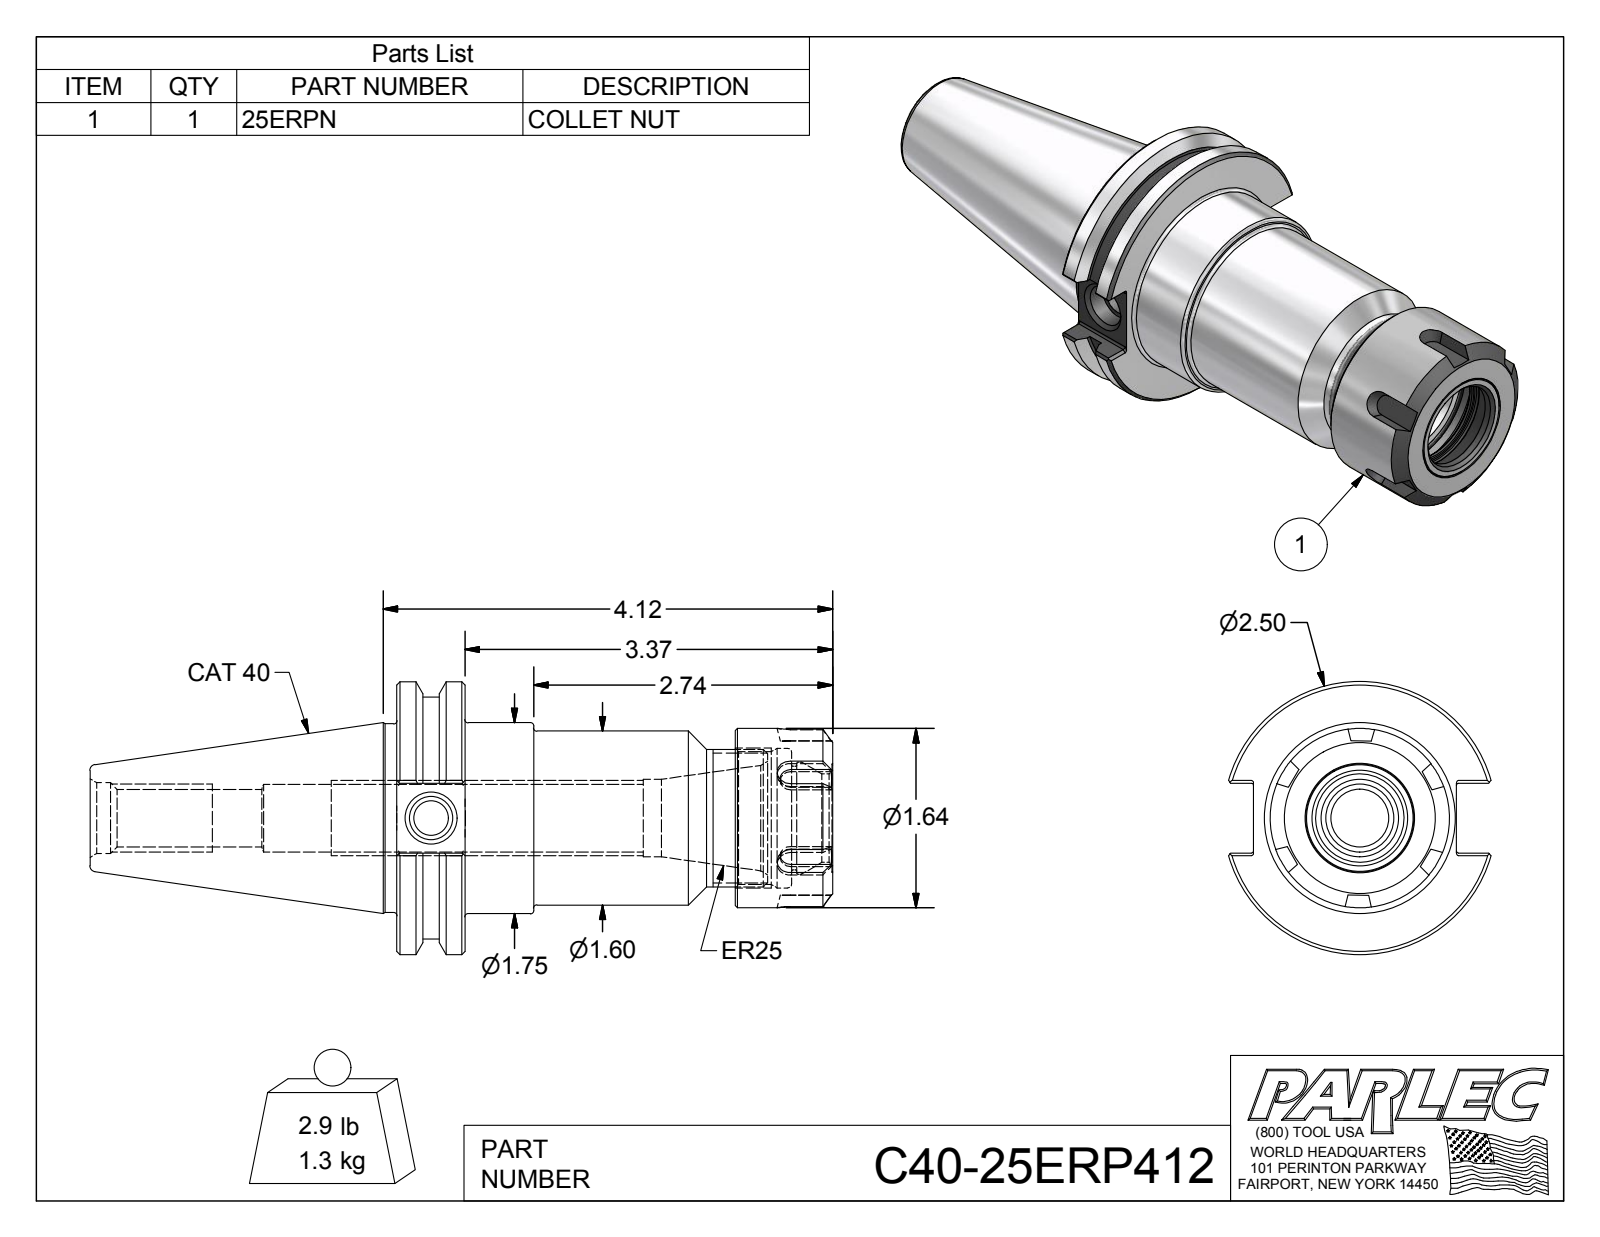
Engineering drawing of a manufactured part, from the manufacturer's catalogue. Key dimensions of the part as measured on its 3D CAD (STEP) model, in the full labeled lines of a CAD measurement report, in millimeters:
Part name (STEP PRODUCT): C40-25ERP412; C40-25ER4-1; 25ERPN
STEP written by: Autodesk Inventor 2012 (AUTOMOTIVE_DESIGN)
Units: millimetres
Bodies: 2 solids, 133 faces (56 planar, 34 cylindrical, 43 other)
Overall size (bounding box): 172.9 × 63.5 × 61
Volume: 181 900 mm³ · Surface area: 39 520 mm²
Round holes (diameter × count): ⌀8 ×1, ⌀10.1 ×1, ⌀13.4 ×1, ⌀15.7 ×1, ⌀16.5 ×1, ⌀18 ×1, ⌀20.6 ×1, ⌀24.1 ×1, ⌀26.1 ×1, ⌀30.9 ×1, ⌀32.5 ×1
Round bosses / shafts (diameter × count): ⌀63.5 ×1, ⌀56.4 ×1, ⌀44.5 ×1, ⌀43.9 ×1, ⌀41.7 ×1, ⌀40.5 ×1, ⌀32 ×1
Partial cylindrical surfaces — rounded edges, fillets, slot ends (radius × count): R0.5 ×12
Main face-to-face distances: 15.9, 101.5, 85.6, 78.8, 62.9, 22.7, 91.9, 76.1, 13.2, 9.5
